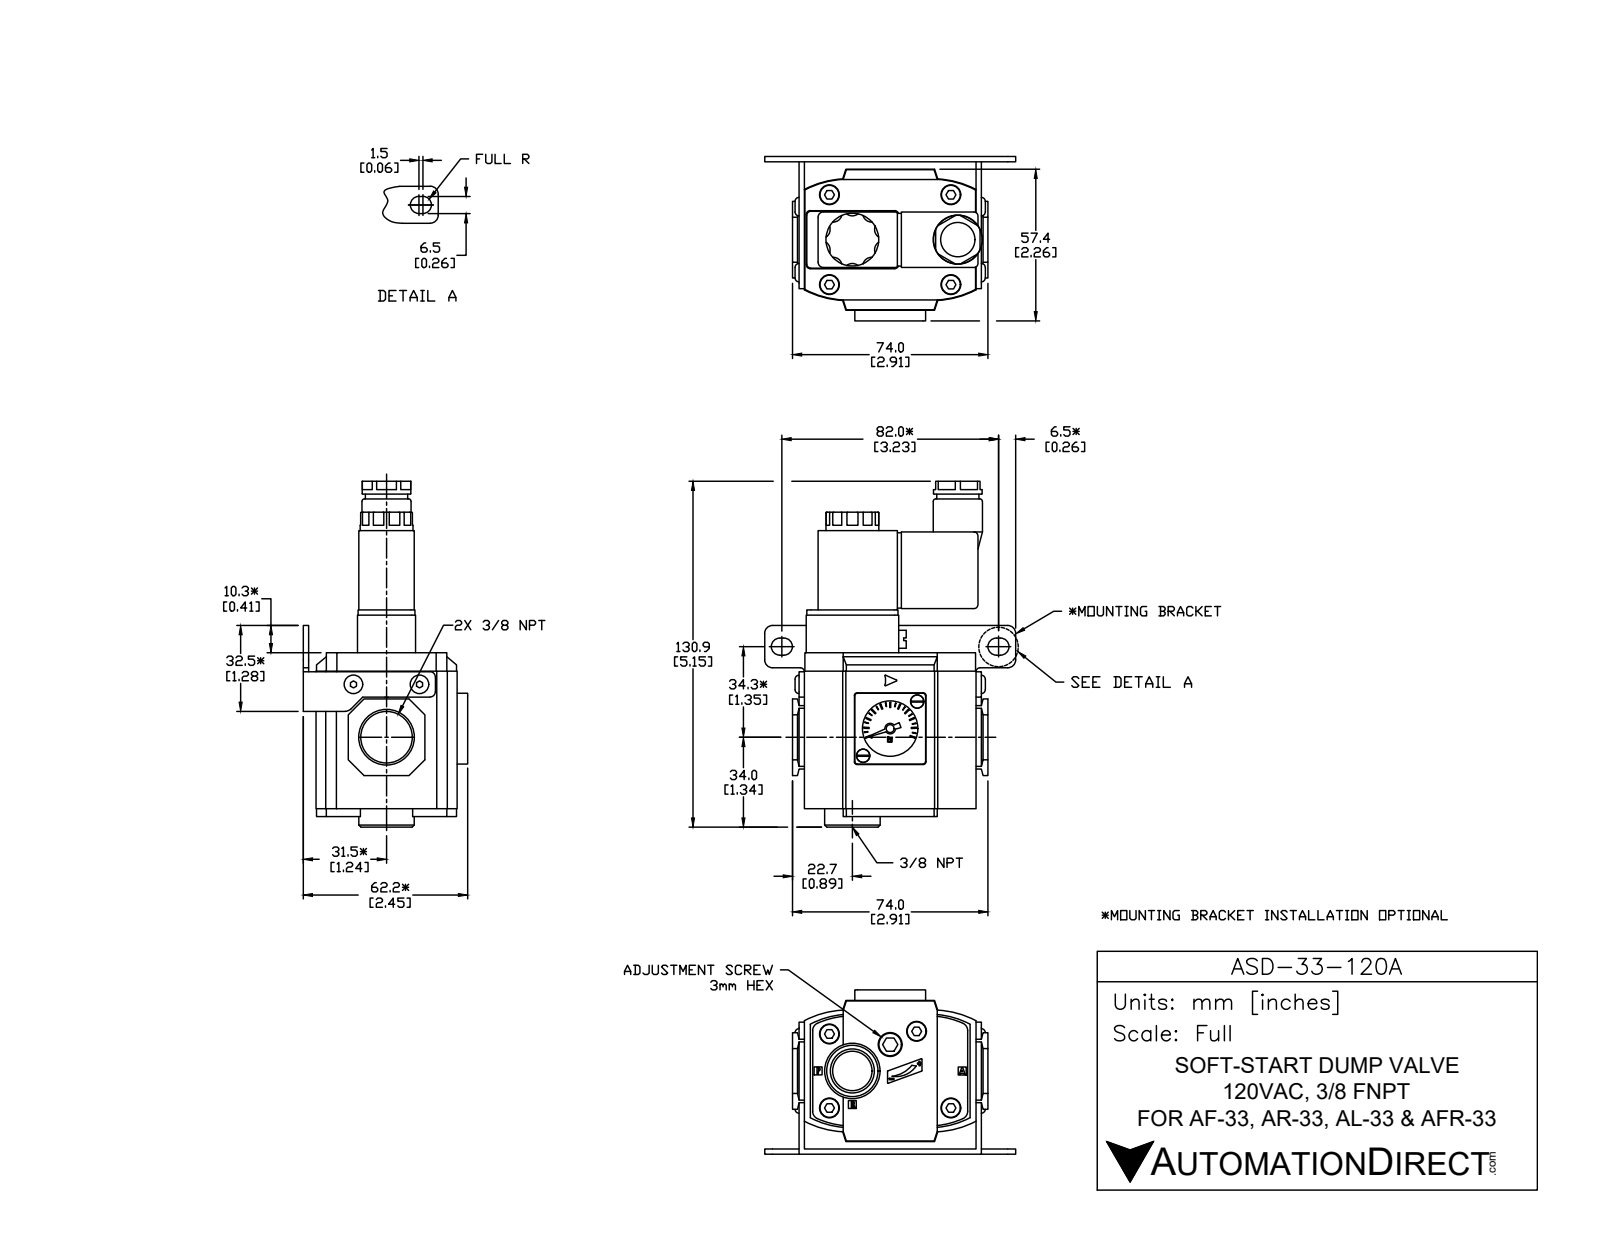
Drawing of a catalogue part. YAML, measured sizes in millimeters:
part_name: "ASD-33-120A"
step_written_by: "SolidWorks 2015 (CONFIG_CONTROL_DESIGN)"
units: millimeters
bodies: {solids: 22, faces: 550, planar: 343, cylindrical: 164, other: 43}
overall_size: [130.9, 95, 62.9]
volume: 253820
surface_area: 60945
round_holes:
  - {diameter: 4, count: 8}
  - {diameter: 7.5, count: 8}
  - {diameter: 3, count: 2}
  - {diameter: 21, count: 2}
  - {diameter: 8.5, count: 1}
  - {diameter: 9, count: 1}
  - {diameter: 13, count: 1}
  - {diameter: 14.27, count: 1}
  - {diameter: 14.95, count: 1}
round_bosses_or_shafts:
  - {diameter: 7.1, count: 8}
  - {diameter: 2.5, count: 2}
  - {diameter: 20, count: 1}
  - {diameter: 18.6, count: 1}
  - {diameter: 18.4, count: 1}
  - {diameter: 16, count: 1}
  - {diameter: 4, count: 1}
partial_cylinders:
  - {radius: 1.5, count: 10}
  - {radius: 3.16, count: 10}
  - {radius: 1, count: 6}
  - {radius: 3, count: 6}
  - {radius: 0.73, count: 4}
  - {radius: 1.25, count: 4}
  - {radius: 3.25, count: 4}
  - {radius: 34.8, count: 4}
face_to_face_distances: [3, 2, 52, 59, 7, 21, 13.2, 34.2, 16.2, 37.2]
hole_center_spacings: [3, 31, 46, 46.1, 55.47, 14.5, 16.48, 17.2]
